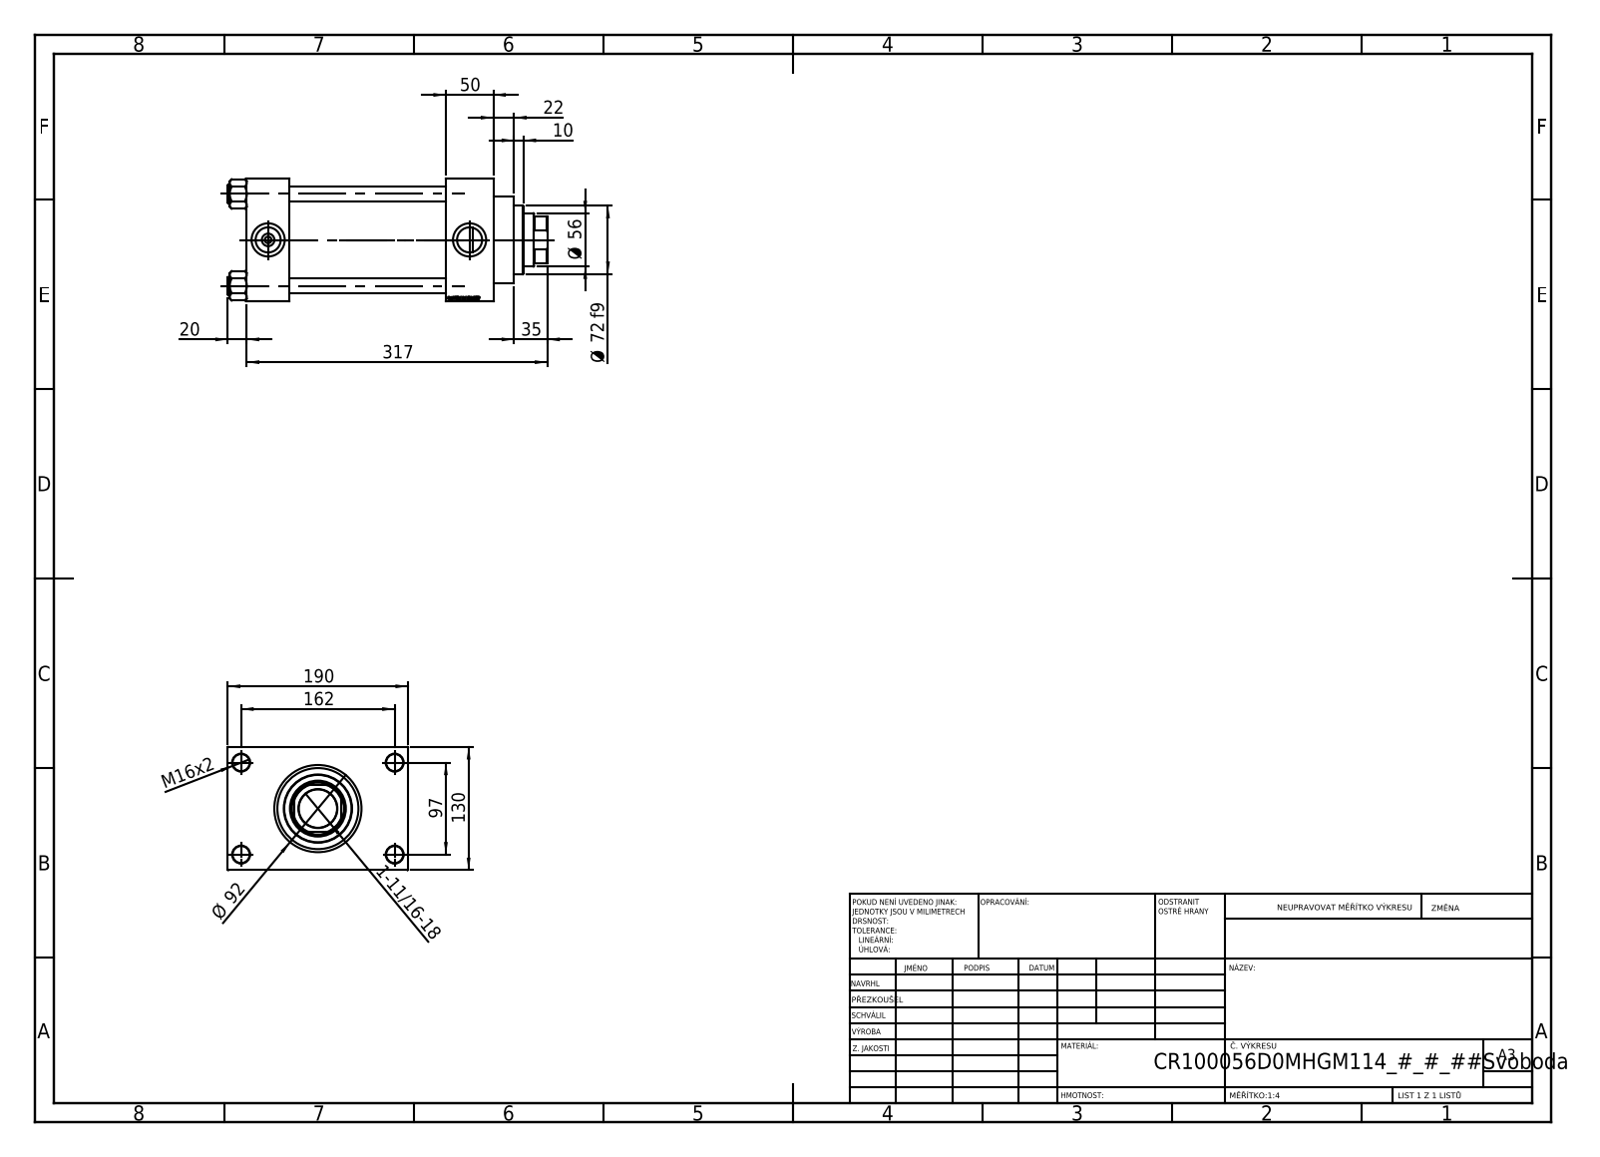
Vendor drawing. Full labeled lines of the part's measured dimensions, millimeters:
Part name (STEP PRODUCT): V215CR_VCP_D; NUT_M5_D; V215CR_D_Body; V215_VC_A (+1 more)
STEP written by: SolidWorks 2019 (CONFIG_CONTROL_DESIGN)
Units: millimetres
Bodies: 11 solids, 1151 faces (545 planar, 88 cylindrical, 518 other)
Overall size (bounding box): 337 × 190 × 130
Volume: 3 026 000 mm³ · Surface area: 458 634 mm²
Round holes (diameter × count): ⌀16 ×4, ⌀18 ×4, ⌀7 ×2, ⌀26.44 ×2, ⌀35 ×2, ⌀40.5 ×1, ⌀56 ×1, ⌀59 ×1, ⌀76 ×1, ⌀85.5 ×1, ⌀100 ×1
Round bosses / shafts (diameter × count): ⌀19 ×4, ⌀106 ×1, ⌀92 ×1, ⌀72 ×1
Partial cylindrical surfaces — rounded edges, fillets, slot ends (radius × count): R27 ×1
Main face-to-face distances: 130, 50, 45, 210, 165, 260, 215, 30, 160, 114
Hole centre spacings: 32.55, 68.52, 94.41, 96.9, 102.27, 129.45, 161.73, 97
